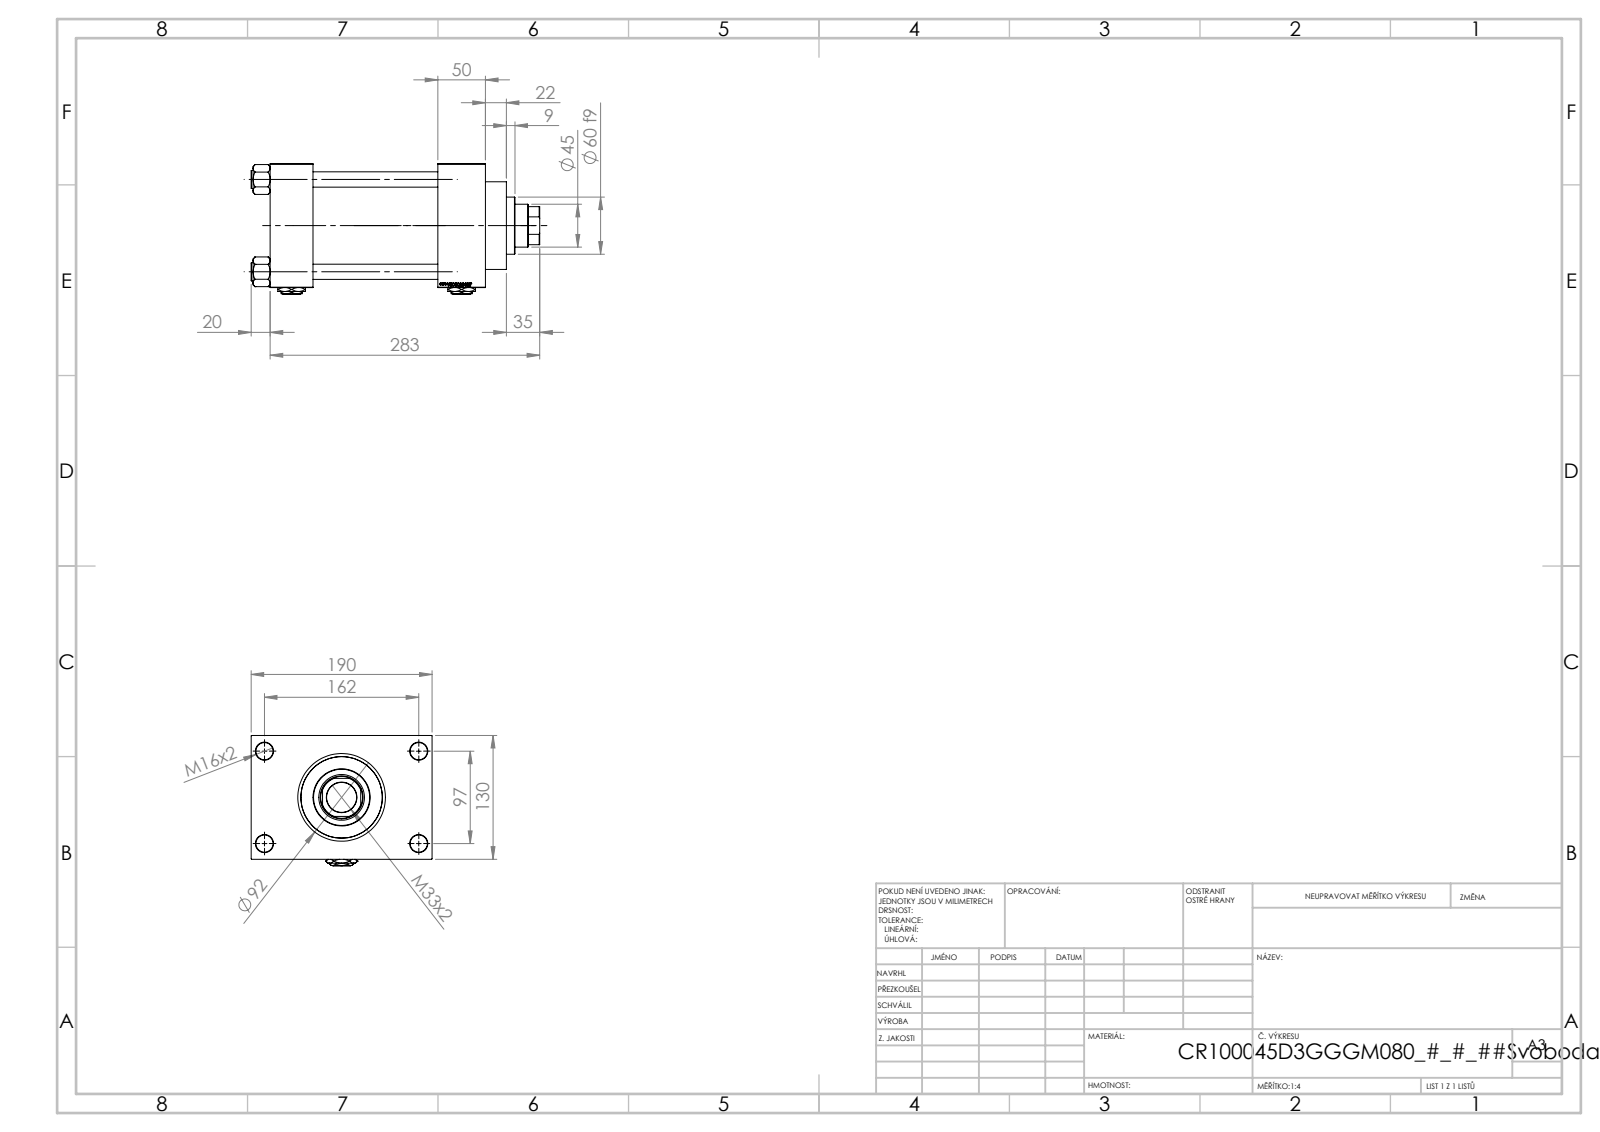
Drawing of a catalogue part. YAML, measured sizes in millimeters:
part_name: "NUT_M5_D; Zatka_pro_OIL_PORT; V215CR_VCP_D; V215_VC_A (+2 more)"
step_written_by: "SolidWorks 2019 (CONFIG_CONTROL_DESIGN)"
units: millimeters
bodies: {solids: 13, faces: 1253, planar: 593, cylindrical: 100, other: 560}
overall_size: [303, 190, 137]
volume: 2794000
surface_area: 418688
round_holes:
  - {diameter: 16, count: 4}
  - {diameter: 18, count: 4}
  - {diameter: 7, count: 2}
  - {diameter: 26.44, count: 2}
  - {diameter: 35, count: 2}
  - {diameter: 31.5, count: 1}
  - {diameter: 45, count: 1}
  - {diameter: 48, count: 1}
  - {diameter: 76, count: 1}
  - {diameter: 85.5, count: 1}
  - {diameter: 100, count: 1}
round_bosses_or_shafts:
  - {diameter: 19, count: 4}
  - {diameter: 106, count: 1}
  - {diameter: 92, count: 1}
  - {diameter: 60, count: 1}
partial_cylinders:
  - {radius: 22, count: 1}
face_to_face_distances: [130, 45, 176, 131, 226, 181, 50, 30, 160, 190]
hole_center_spacings: [32.55, 68.52, 94.41, 96.9, 102.27, 129.45, 161.73, 97]
